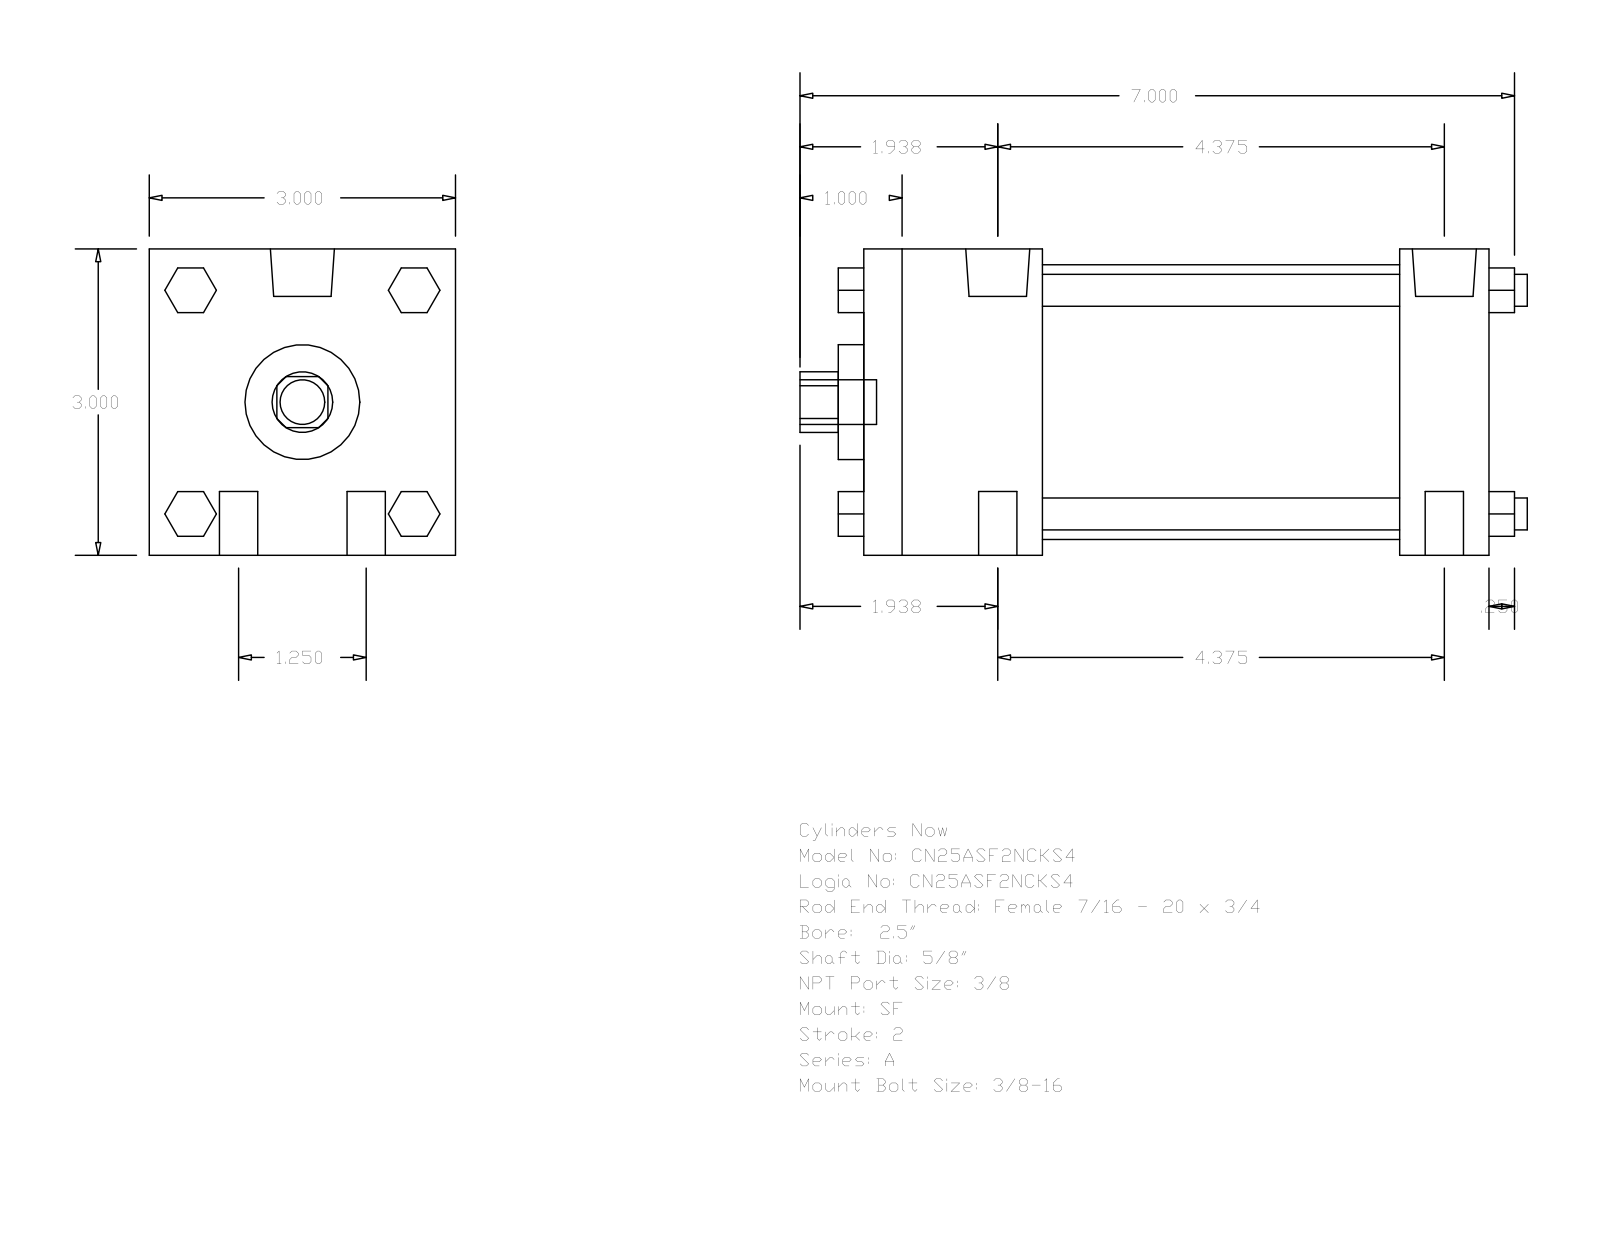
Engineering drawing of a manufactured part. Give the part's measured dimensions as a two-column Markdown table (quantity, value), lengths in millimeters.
| quantity | value |
| --- | --- |
| part name | A_SF__0250_0.625 |
| STEP written by | GSSL Pune (CONFIG_CONTROL_DESIGN) |
| units | millimeters |
| bodies | 0 solids, 124 faces (94 planar, 30 cylindrical, 0 other) |
| overall size | 180.97 × 76.2 × 76.2 |
| round holes (diameter × count) | 15.88 × 1, 28.57 × 1, 68.33 × 1 |
| round bosses / shafts (diameter × count) | 9.53 × 4, 7.94 × 4, 15.93 × 2, 5.56 × 2, 11.11 × 1 |
| partial cylindrical surfaces (radius × count) | 7.54 × 1 |
| main face-to-face distances | 76.2, 155.57, 44.45, 133.34, 22.23, 88.89, 111.12, 161.92, 6.35, 50.8 |
